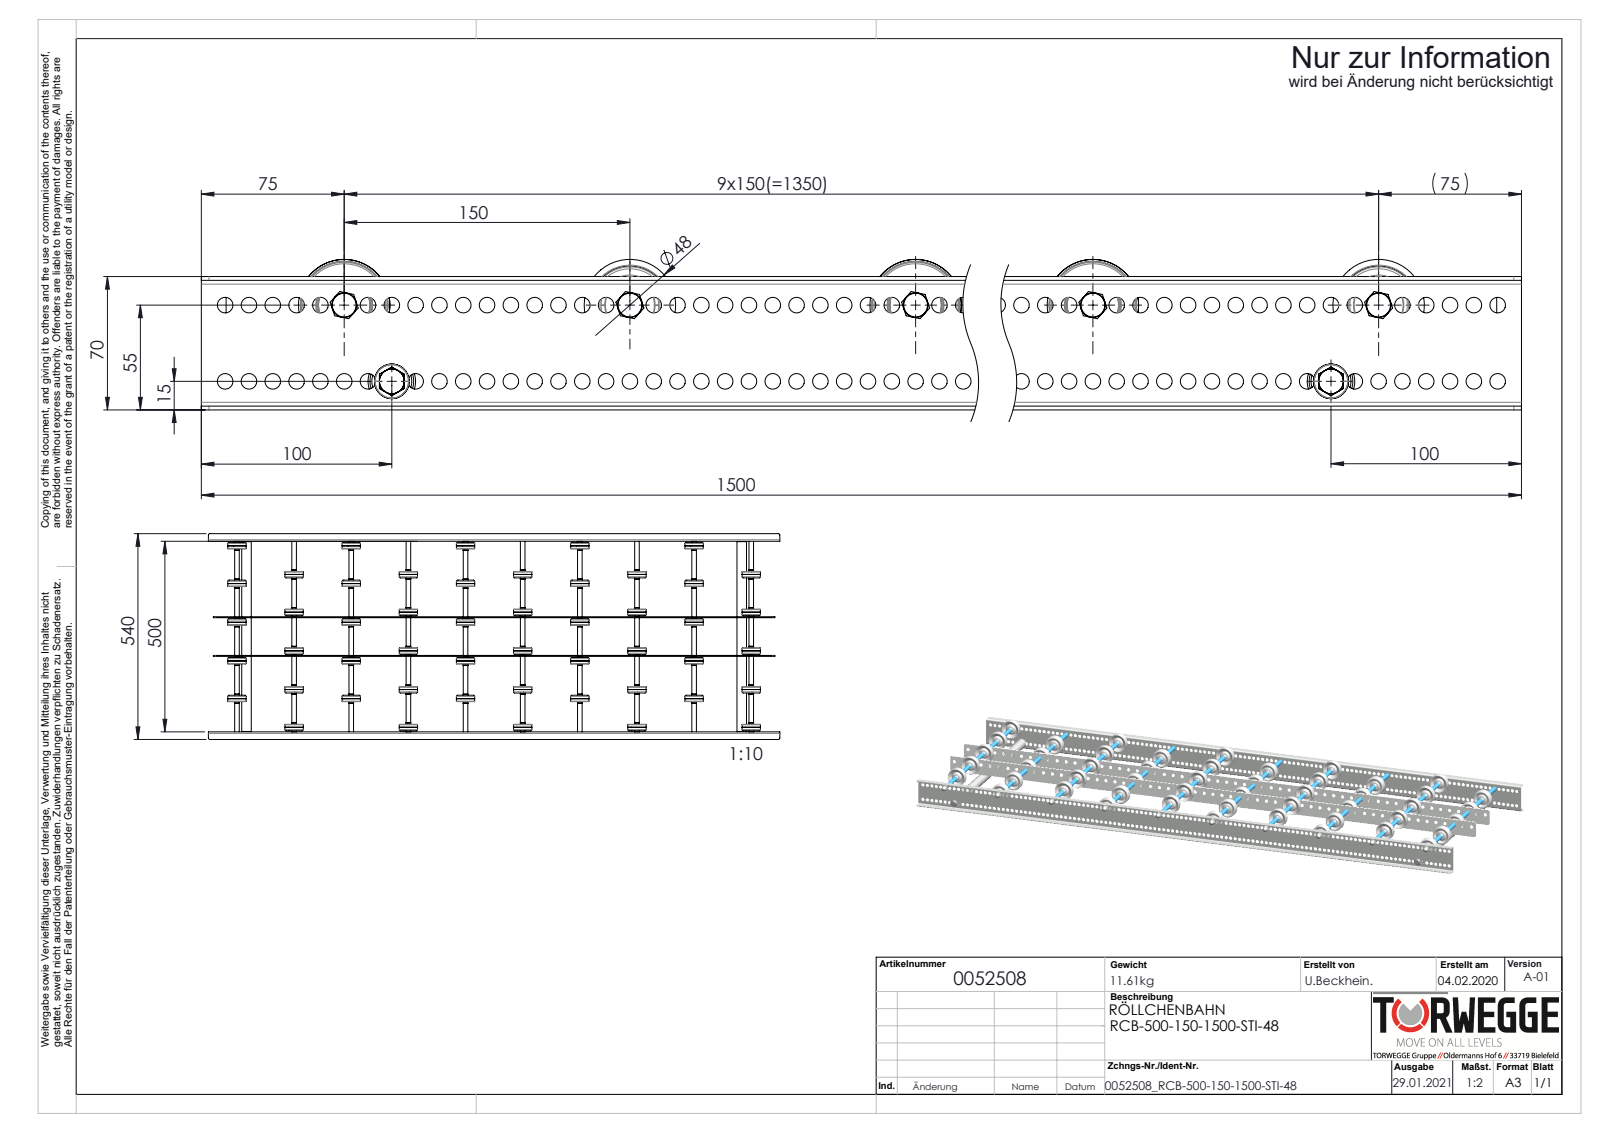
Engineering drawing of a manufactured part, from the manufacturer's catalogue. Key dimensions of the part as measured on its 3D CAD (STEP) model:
Part name (STEP PRODUCT): S100100_Längstraverse-42x2,5_S100102_Lngstraverse-RB-L1500; 0046278_KB-ROHR-12X1,75mm_KFG_L75; Traversen_KFG_L500; K0011528_2200-48-8 (+6 more)
STEP written by: SolidWorks 2020 (AUTOMOTIVE_DESIGN)
Units: millimetres
Bodies: 194 solids, 6428 faces (1212 planar, 2852 cylindrical, 2364 other)
Overall size (bounding box): 1500 × 540 × 79
Volume: 2 515 000 mm³ · Surface area: 2 043 000 mm²
Round holes (diameter × count): ⌀8.2 ×238, ⌀8.5 ×59, ⌀6.65 ×10, ⌀8 ×10, ⌀9.65 ×10, ⌀15 ×10, ⌀41 ×10, ⌀6.8 ×2, ⌀21 ×2
Round bosses / shafts (diameter × count): ⌀48 ×10, ⌀13 ×10, ⌀12.5 ×10, ⌀12.4 ×10, ⌀12 ×10, ⌀11.5 ×10, ⌀25 ×2, ⌀8 ×2
Partial cylindrical surfaces — rounded edges, fillets, slot ends (radius × count): R4 ×8, R2 ×4, R5 ×4
Main face-to-face distances: 2, 200.5, 302, 101.5, 502, 99, 200, 202.5, 301.5, 304
Hole centre spacings: 12.5, 25, 37.5, 50, 62.5, 75, 87.5, 100
